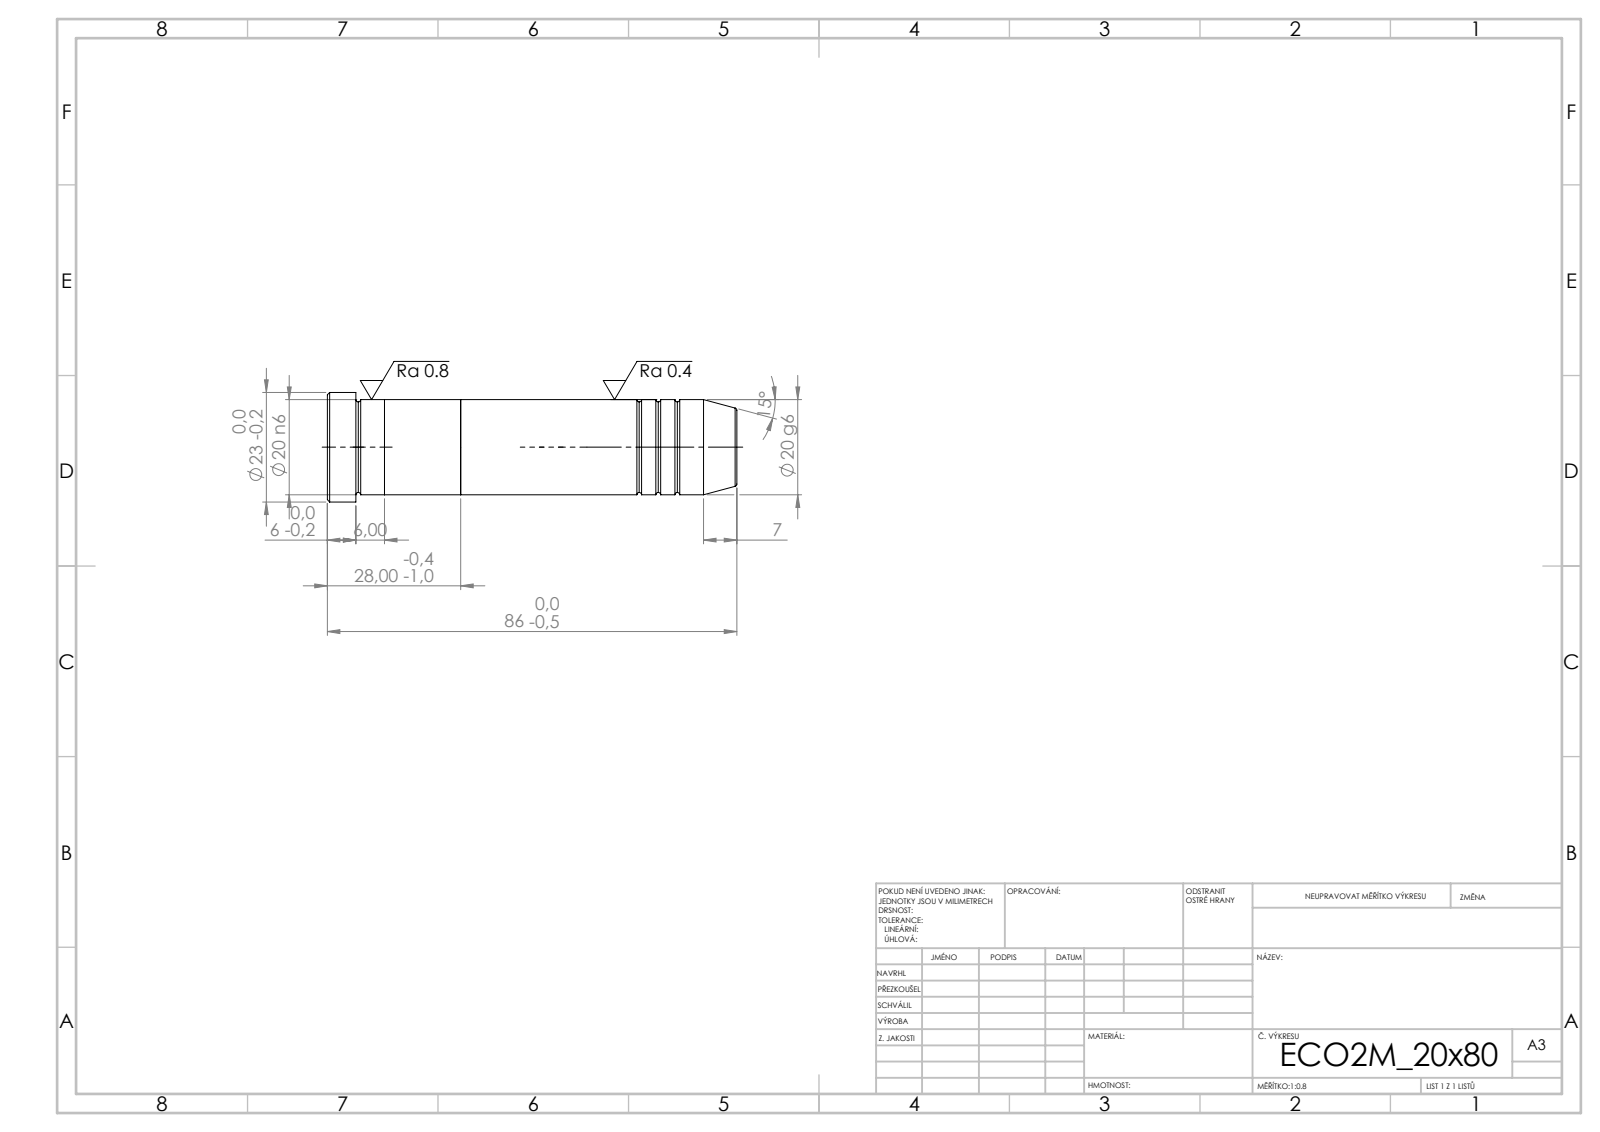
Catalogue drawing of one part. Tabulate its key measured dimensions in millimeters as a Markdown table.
| quantity | value |
| --- | --- |
| STEP written by | SolidWorks 2019 (CONFIG_CONTROL_DESIGN) |
| units | millimeters |
| bodies | 3 solids, 43 faces (7 planar, 14 cylindrical, 22 other) |
| overall size | 86 × 23 × 23 |
| volume | 27 132 mm³ |
| surface area | 7 517 mm² |
| round bosses / shafts (diameter × count) | 23 × 1, 20 × 1 |
| main face-to-face distances | 16, 28, 12, 6, 58, 74, 86, 80, 22 |
